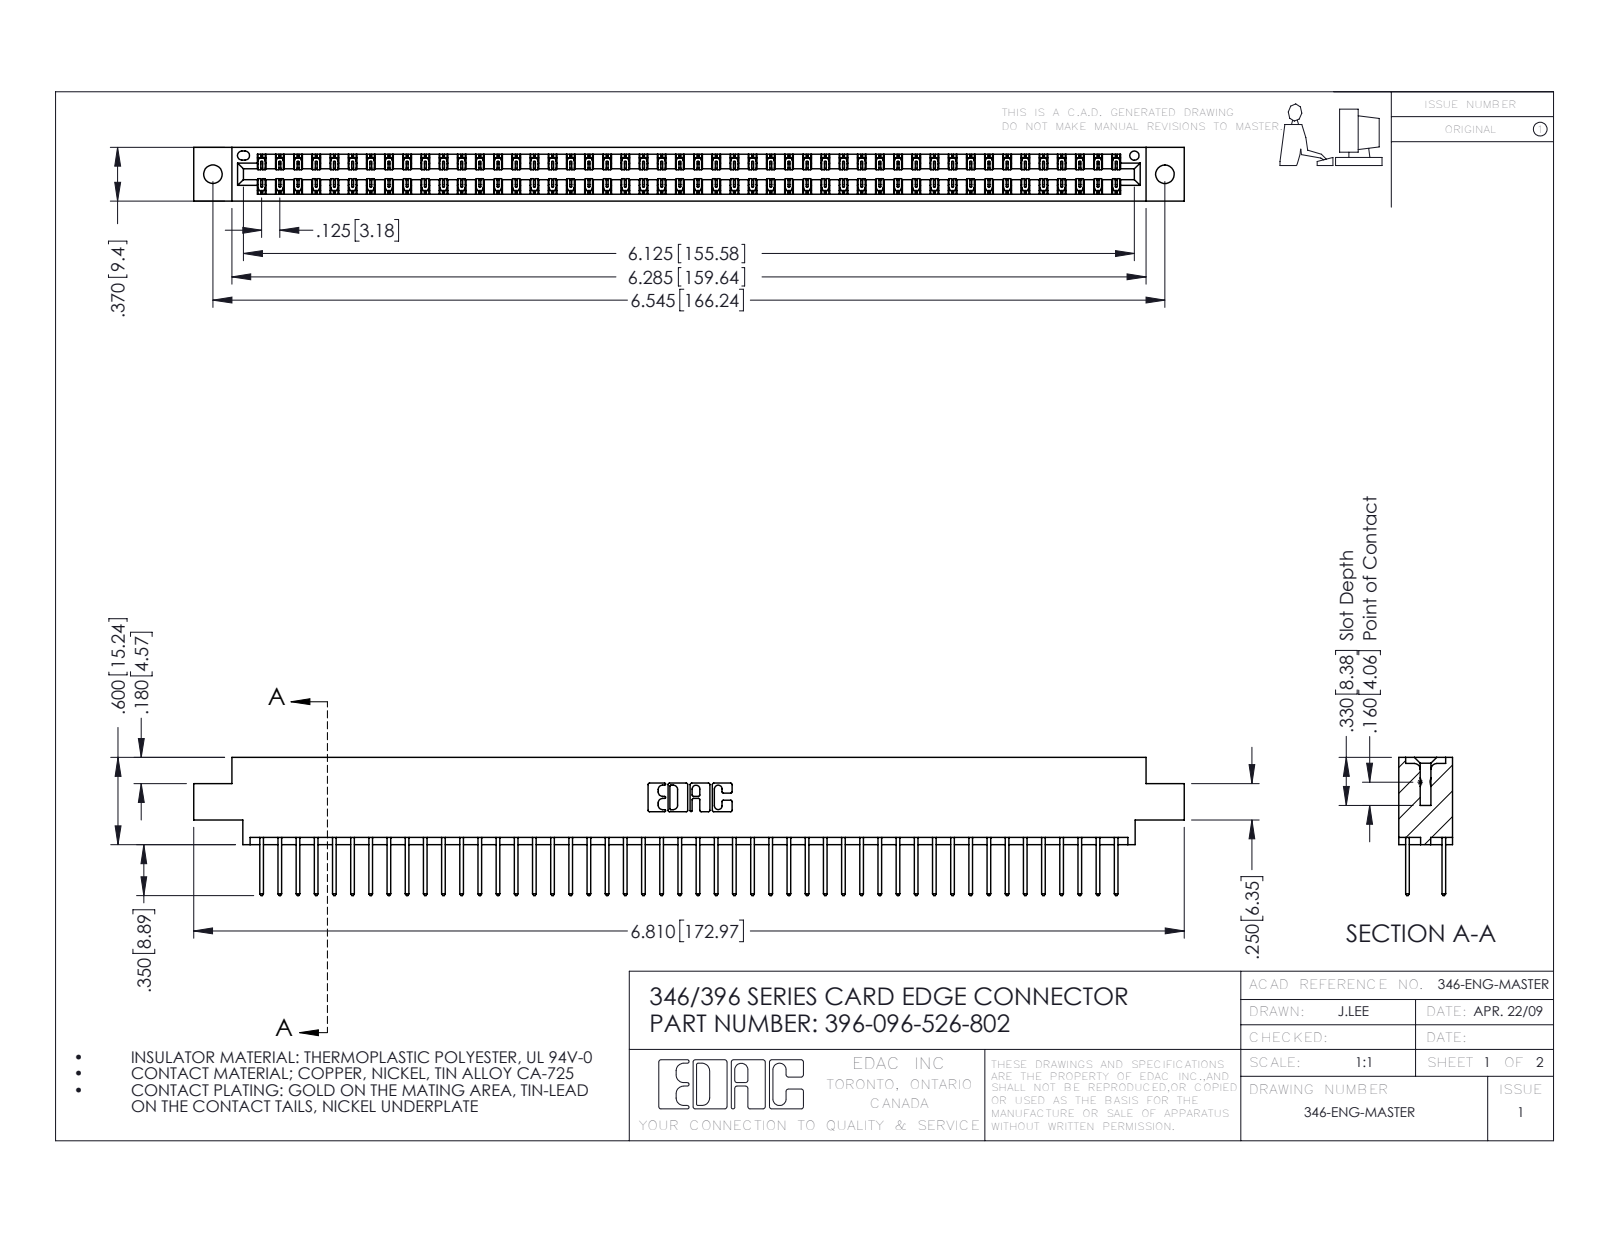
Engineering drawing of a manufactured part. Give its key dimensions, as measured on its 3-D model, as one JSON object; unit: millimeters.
{"part_name": "396-096-526-802; 345-292-001_345-293-126; 346 Part_0.170 Offset - 0.128 Dia", "step_written_by": "SolidWorks 2016 (CONFIG_CONTROL_DESIGN)", "units": "millimeters", "bodies": {"solids": 97, "faces": 5118, "planar": 3440, "cylindrical": 1678, "other": 0}, "overall_size": [173, 24.1, 9.4], "volume_mm3": 16880, "surface_area_mm2": 23910, "round_holes": [[3.3, 2], [1.6, 1]], "partial_cylinders_radius": [[0.2, 144], [0.3, 96], [0.3, 22], [0.2, 6], [0.8, 6], [0.7, 3], [0.4, 2], [0.6, 2]], "face_to_face_distances": [1.2, 8.2, 6.4, 9.4, 1.8, 7.6, 0.6, 7, 3.8, 5.6], "hole_center_spacings": [6.2, 160.9, 166.2]}
